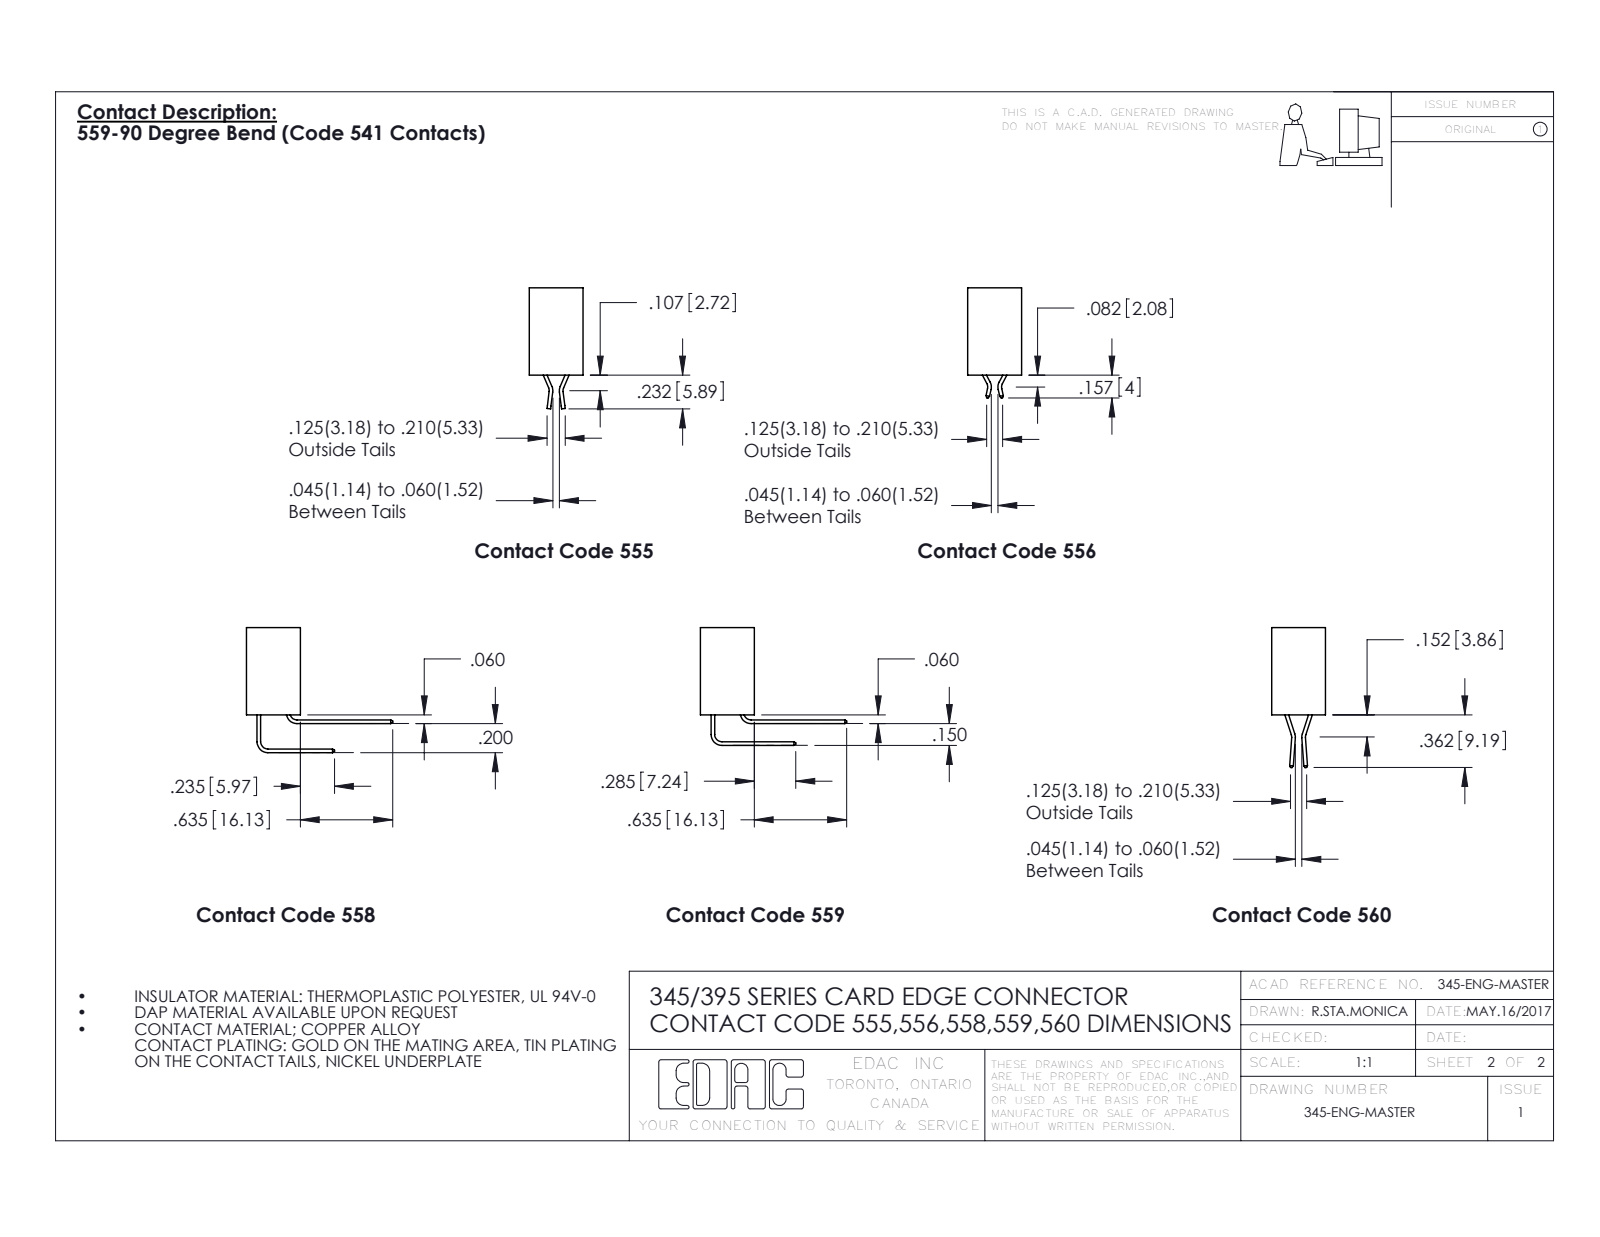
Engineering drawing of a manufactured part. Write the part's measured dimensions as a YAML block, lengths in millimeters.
part_name: "395-120-555-212; 345 Part_Flush Mounting Lugs - Side Mount; 345-292-001_555 Tail"
step_written_by: "SolidWorks 2016 (CONFIG_CONTROL_DESIGN)"
units: millimeters
bodies: {solids: 121, faces: 6846, planar: 3800, cylindrical: 3046, other: 0}
overall_size: [173.6, 21.1, 9.4]
volume: 17290
surface_area: 26990
round_holes:
  - {diameter: 3.3, count: 2}
  - {diameter: 1.6, count: 1}
partial_cylinders:
  - {radius: 0.4, count: 300}
  - {radius: 0.5, count: 240}
  - {radius: 0.2, count: 180}
  - {radius: 0.3, count: 22}
  - {radius: 0.2, count: 6}
  - {radius: 0.8, count: 6}
  - {radius: 0.7, count: 3}
  - {radius: 0.3, count: 2}
face_to_face_distances: [7.6, 1.8, 0.6, 9.4, 5.1, 2.5, 6.9, 5.7, 4.4, 3.8]
hole_center_spacings: [167]
